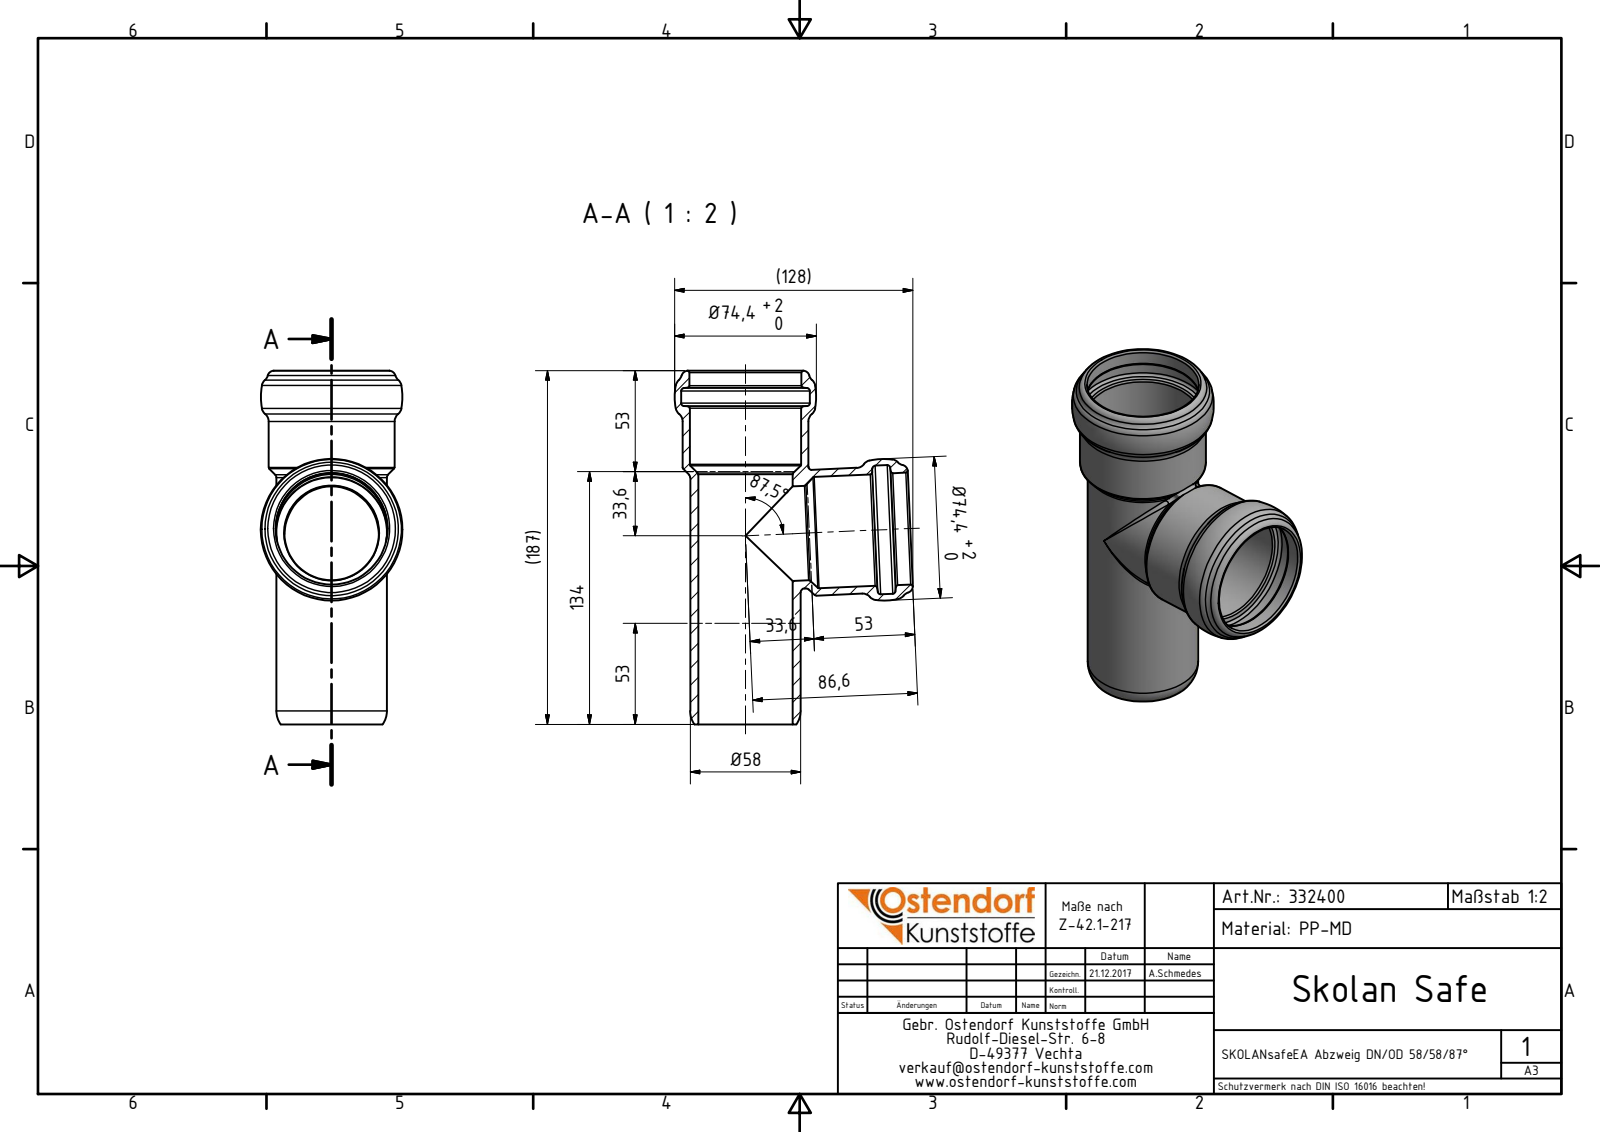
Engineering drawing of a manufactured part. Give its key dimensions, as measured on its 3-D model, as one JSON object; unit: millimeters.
{"part_name": "332400 SKOLANsafeEA Abzweiger DN_OD 58_58_87°", "step_written_by": "Autodesk Inventor 2016 (AUTOMOTIVE_DESIGN)", "units": "millimeters", "bodies": {"solids": 1, "faces": 58, "planar": 1, "cylindrical": 12, "other": 45}, "overall_size": [185.6, 125.05, 74.4], "volume_mm3": 186317, "surface_area_mm2": 93148, "round_holes": [[49.6, 2], [58.5, 2], [58.8, 2], [67.6, 2]], "round_bosses_or_shafts": [[66.1, 2], [58, 2]]}
